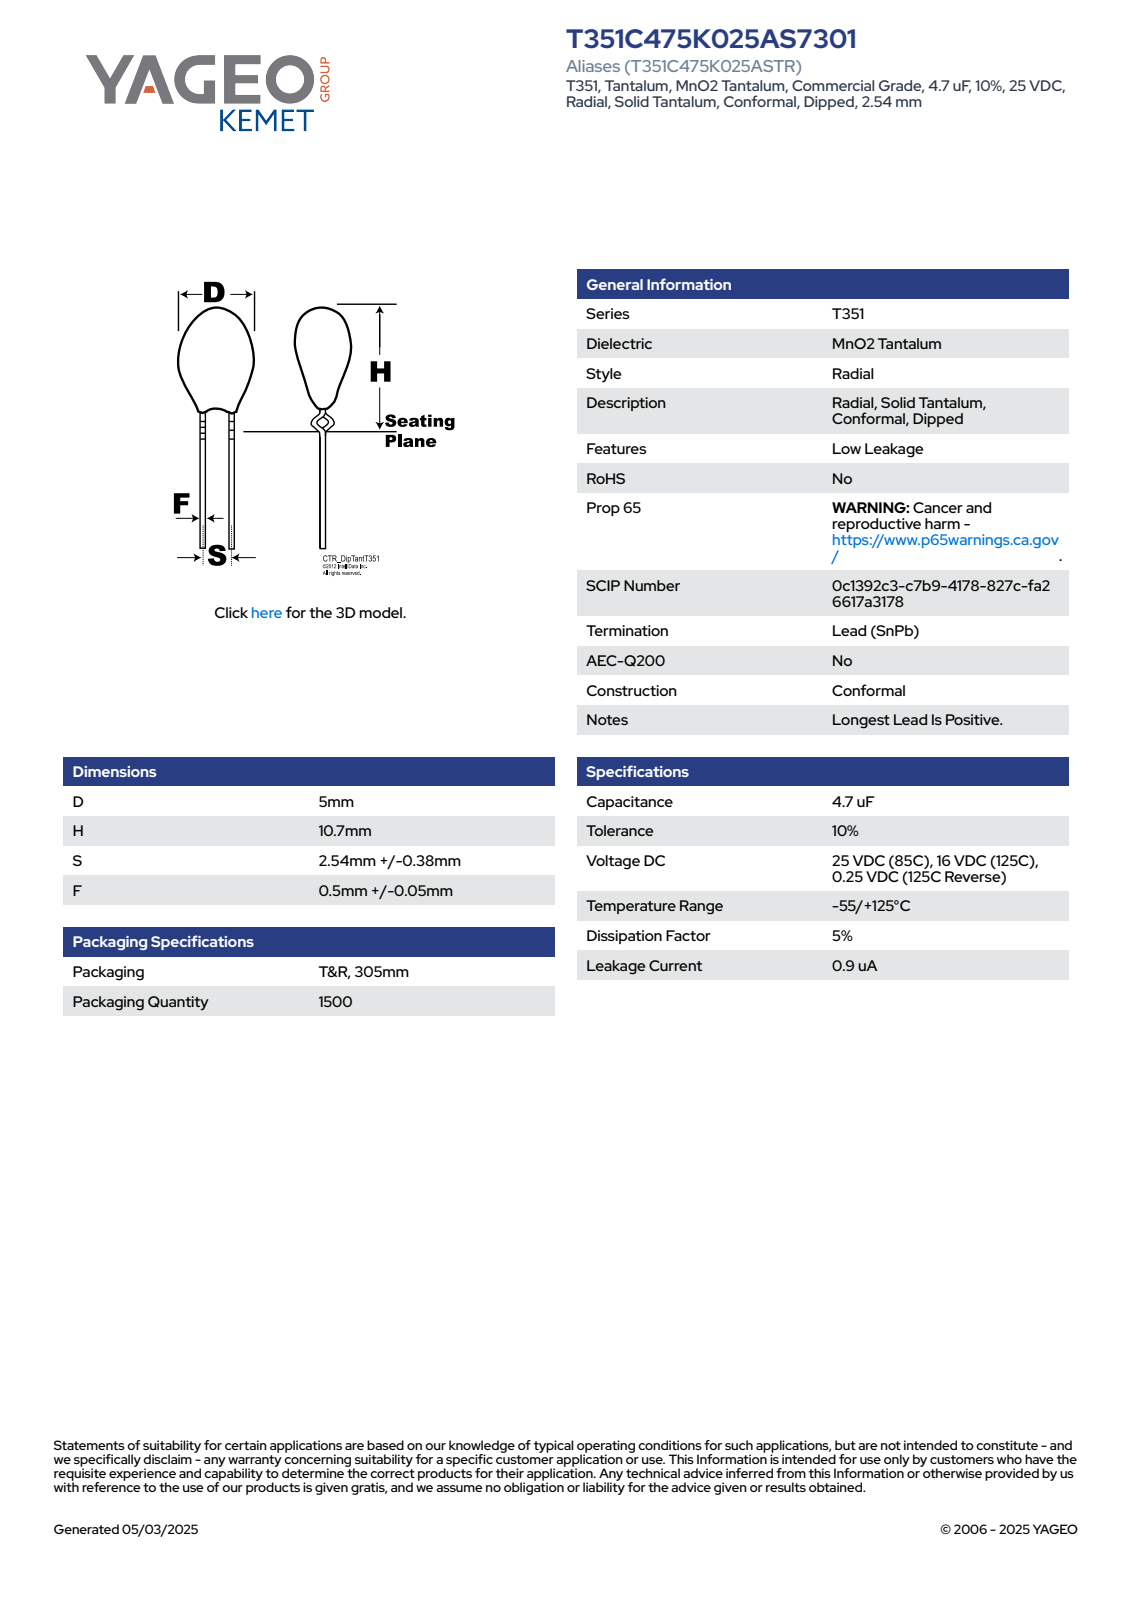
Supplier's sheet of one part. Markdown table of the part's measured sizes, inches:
| quantity | value |
| --- | --- |
| part name | CTR_T351_D5H10.7S2.54LL5.56F0.55 |
| STEP written by | SolidWorks 2014 (AUTOMOTIVE_DESIGN) |
| units | inches |
| bodies | 1 solid, 87 faces (27 planar, 9 cylindrical, 51 other) |
| overall size | 0.64 × 0.197 × 0.197 |
| volume | 0.008 in³ |
| surface area | 0.25 in² |
| round bosses / shafts (diameter × count) | 0.022 × 2, 0.197 × 1 |
| partial cylindrical surfaces (radius × count) | 0.098 × 1 |
| main face-to-face distances | 0.333, 0.501, 0.168, 0.469, 0.136, 0.032, 0.475, 0.142, 0.026, 0.64 |
